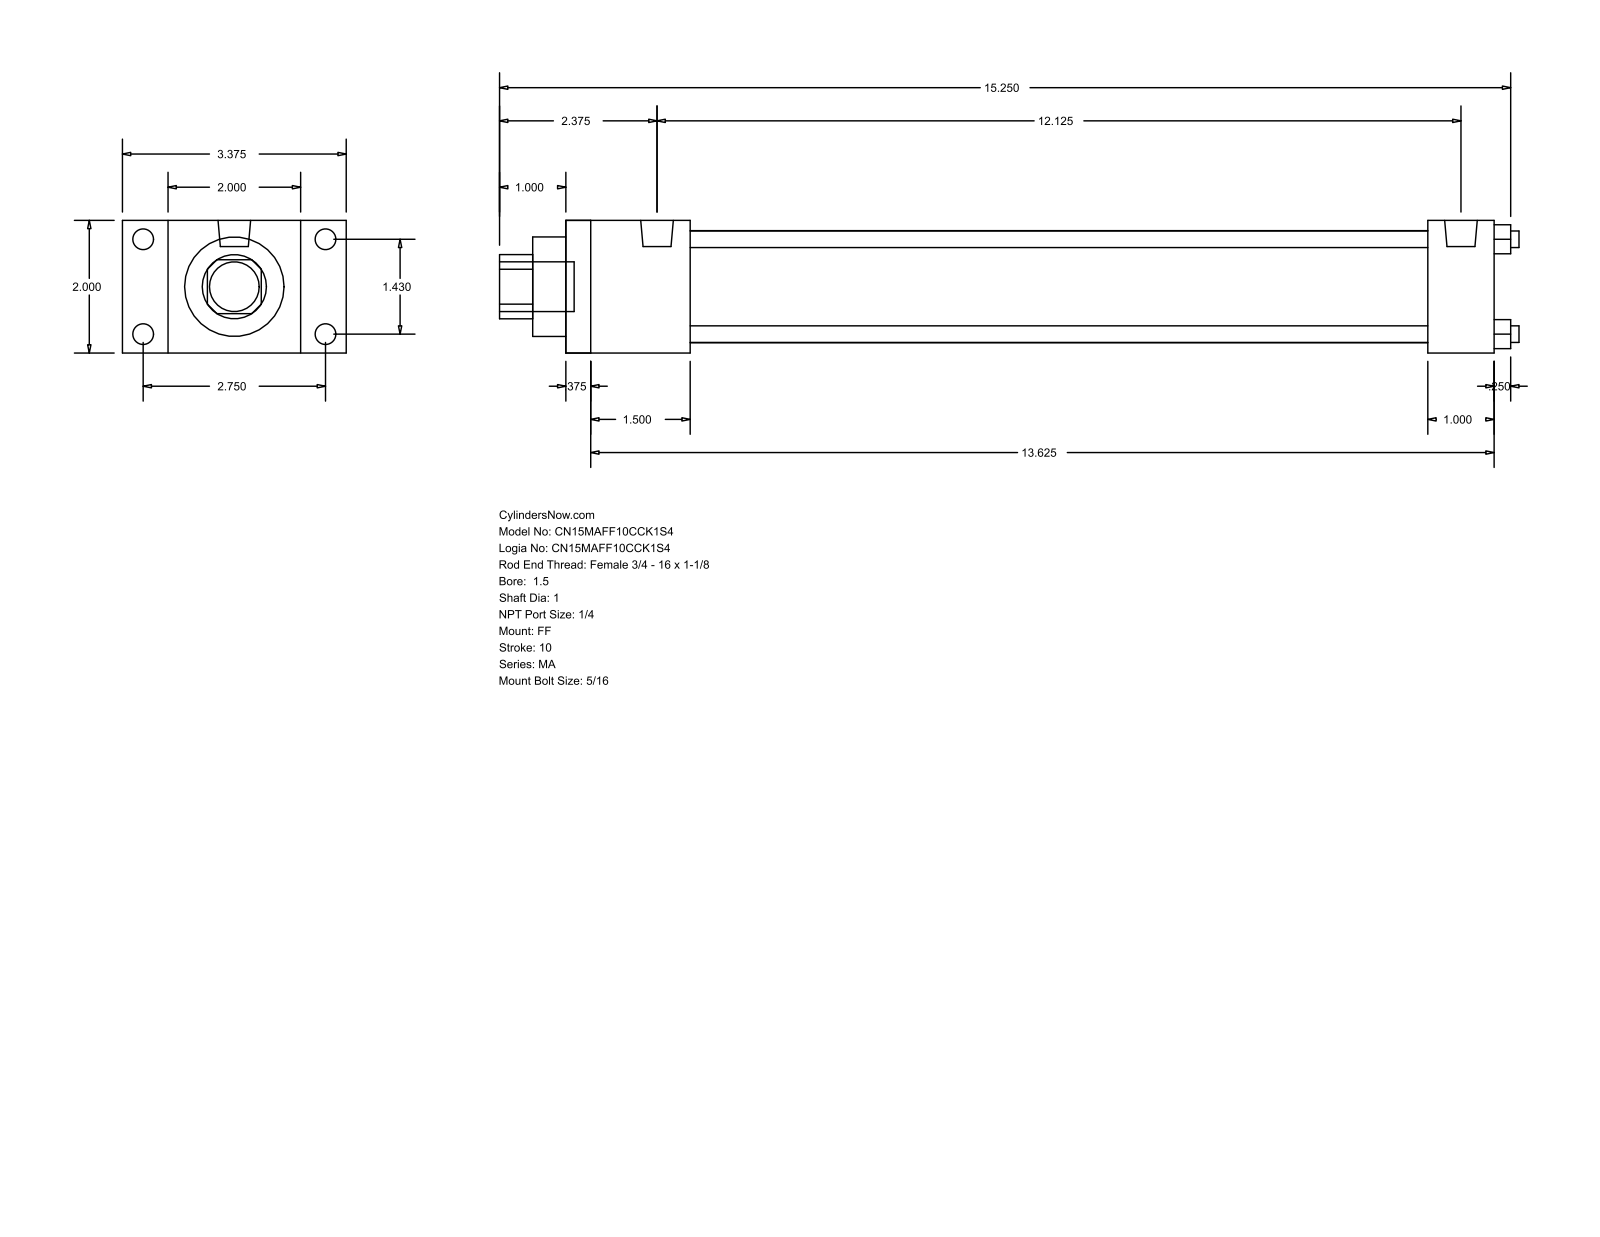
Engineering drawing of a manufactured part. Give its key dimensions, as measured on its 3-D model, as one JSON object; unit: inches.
{"part_name": "MA_FF__0150_1", "step_written_by": "GSSL Pune (CONFIG_CONTROL_DESIGN)", "units": "inches", "bodies": {"solids": 0, "faces": 92, "planar": 64, "cylindrical": 28, "other": 0}, "overall_size": [15.375, 3.375, 2], "round_holes": [[0.25, 4], [1, 1], [1.5, 1], [1.69, 1]], "round_bosses_or_shafts": [[0.313, 8], [0.492, 2], [0.75, 1]], "partial_cylinders_radius": [[0.484, 1]], "face_to_face_distances": [2, 14, 0.375, 13.625, 1, 1.875, 13, 1.5, 12.625, 11.125], "hole_center_spacings": [1.011, 1.43, 2.022]}
